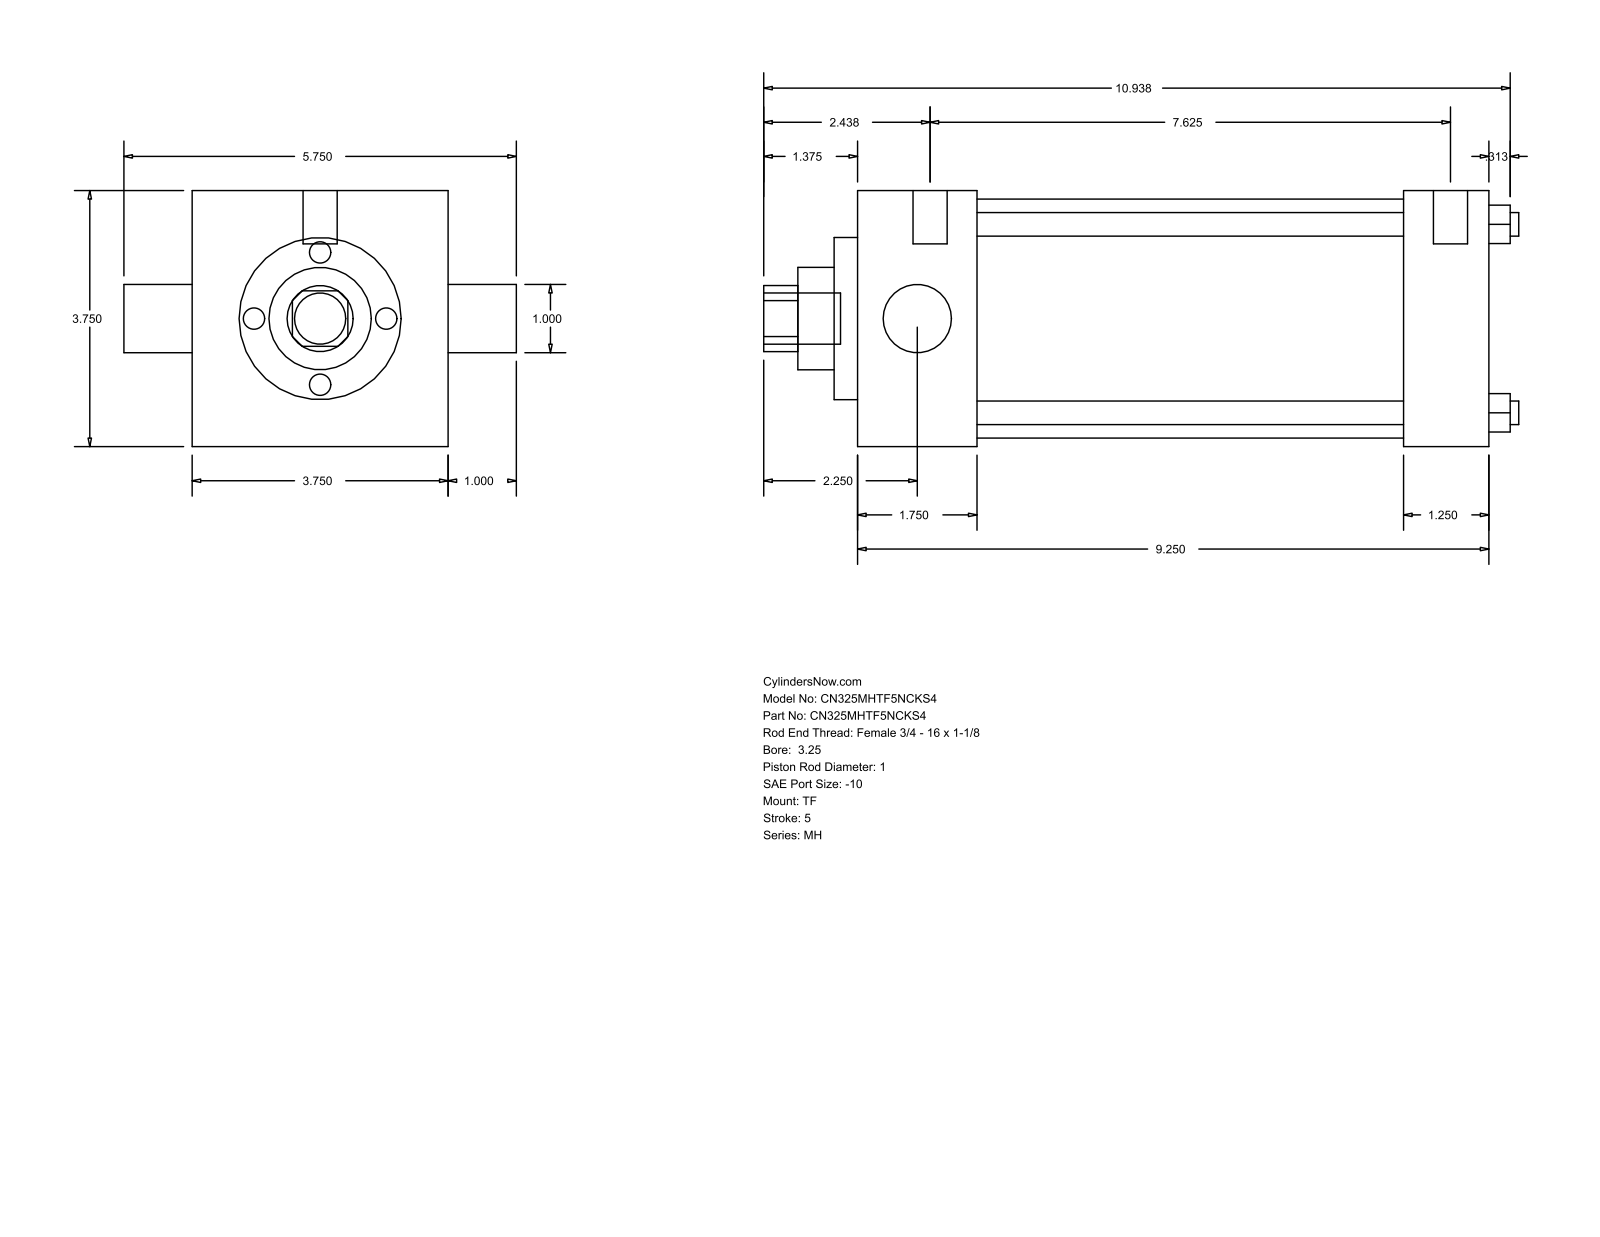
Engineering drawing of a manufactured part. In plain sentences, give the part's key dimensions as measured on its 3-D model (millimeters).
The part is named "MH_TF__0325_1". Its 3-D file was written by "GSSL Pune (CONFIG_CONTROL_DESIGN)". It is 0 solids with 86 faces: 61 planar, 25 cylindrical and 0 other. Overall it measures 280.99 by 146.05 by 95.25 millimeters. Round holes: 4 of diameter 8.76, 2 of diameter 25.4, 1 of diameter 38.1, 1 of diameter 60.33, 1 of diameter 88.9. Round bosses or shafts: 3 of diameter 5.56, 2 of diameter 12.7, 1 of diameter 19.05. Partial cylindrical surfaces (rounded edges, fillets, slot ends): 1 of radius 12.29. The main face-to-face distances are 95.24, 234.96, 44.46, 203.2, 158.74, 190.5, 31.76, 8.73, 53.19, 211.93. The hole center spacings are 49.57, 70.1, 99.14.
